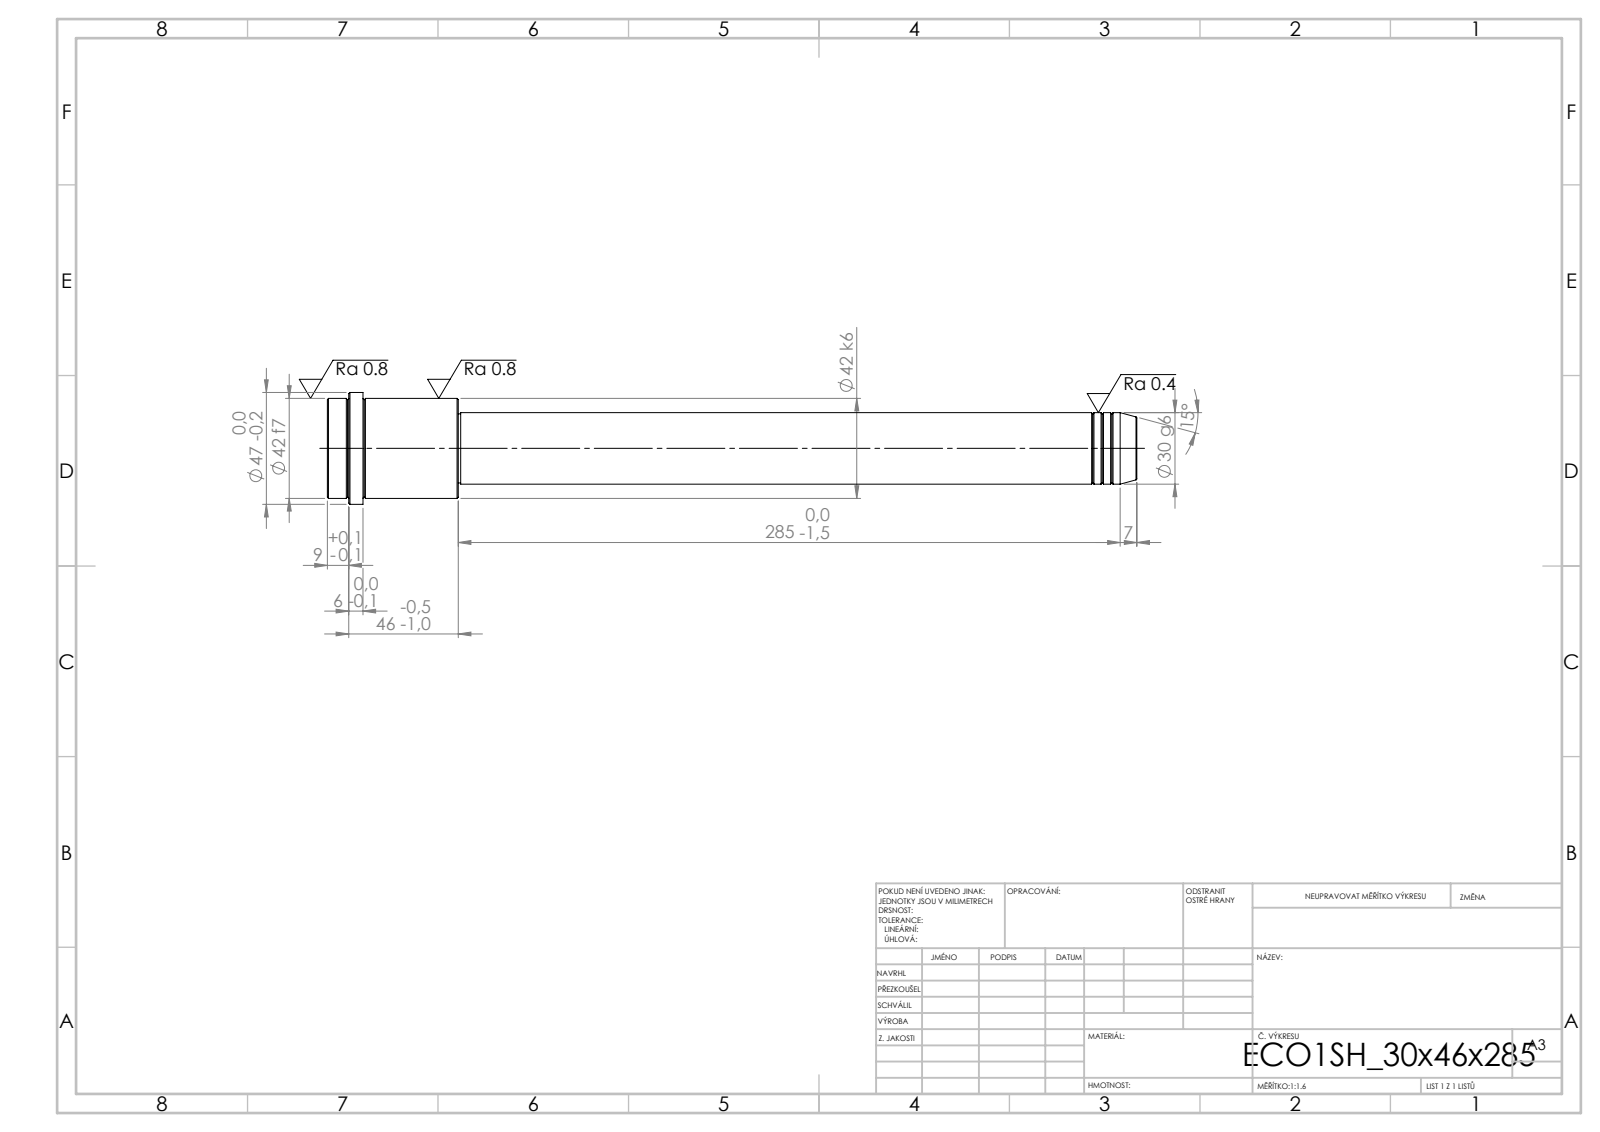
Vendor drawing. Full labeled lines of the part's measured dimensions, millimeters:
STEP written by: SolidWorks 2019 (CONFIG_CONTROL_DESIGN)
Units: millimetres
Bodies: 1 solid, 52 faces (6 planar, 16 cylindrical, 30 other)
Overall size (bounding box): 340 × 47 × 47
Volume: 278 846 mm³ · Surface area: 37 752 mm²
Round bosses / shafts (diameter × count): ⌀47 ×1, ⌀42 ×1, ⌀30 ×1, ⌀29 ×1
Main face-to-face distances: 55, 285, 340, 325, 40, 15, 331, 46, 6, 9
